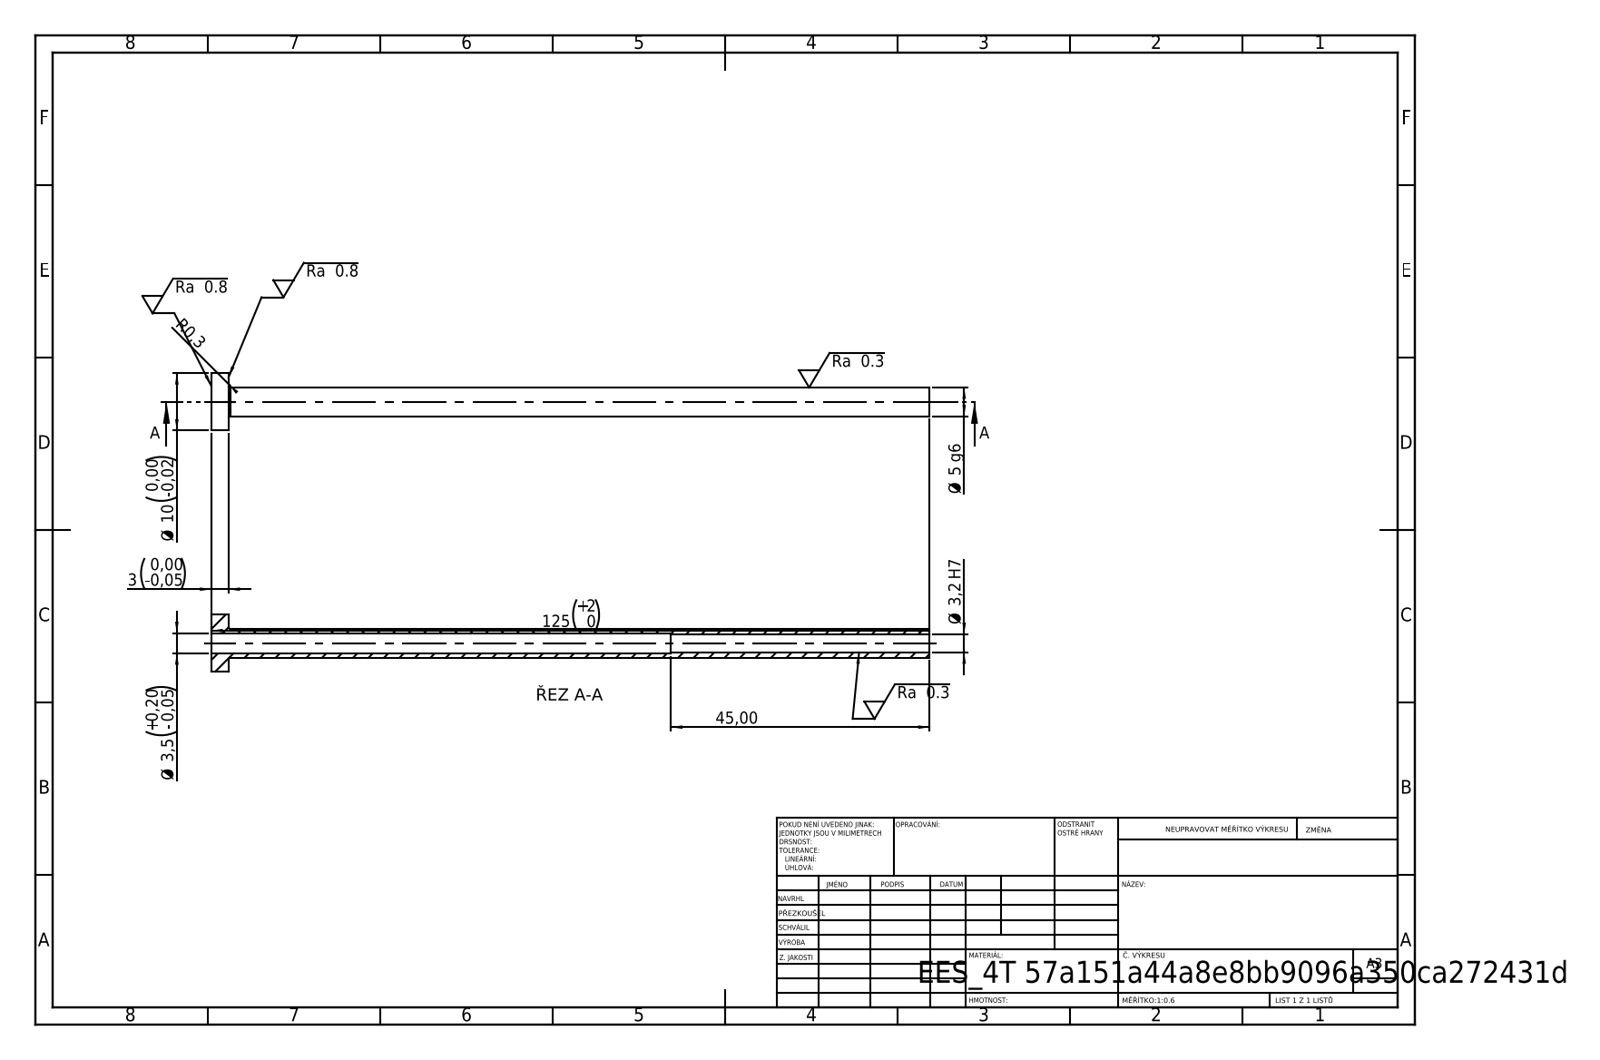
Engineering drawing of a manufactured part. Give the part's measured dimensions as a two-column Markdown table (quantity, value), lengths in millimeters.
| quantity | value |
| --- | --- |
| STEP written by | SolidWorks 2019 (CONFIG_CONTROL_DESIGN) |
| units | millimeters |
| bodies | 1 solid, 14 faces (4 planar, 8 cylindrical, 2 other) |
| overall size | 125 × 10 × 10 |
| volume | 1 500 mm³ |
| surface area | 3 482 mm² |
| round holes (diameter × count) | 3.2 × 1, 3.5 × 1 |
| round bosses / shafts (diameter × count) | 10 × 1, 5 × 1 |
| main face-to-face distances | 3, 125, 122, 80, 77, 45 |
